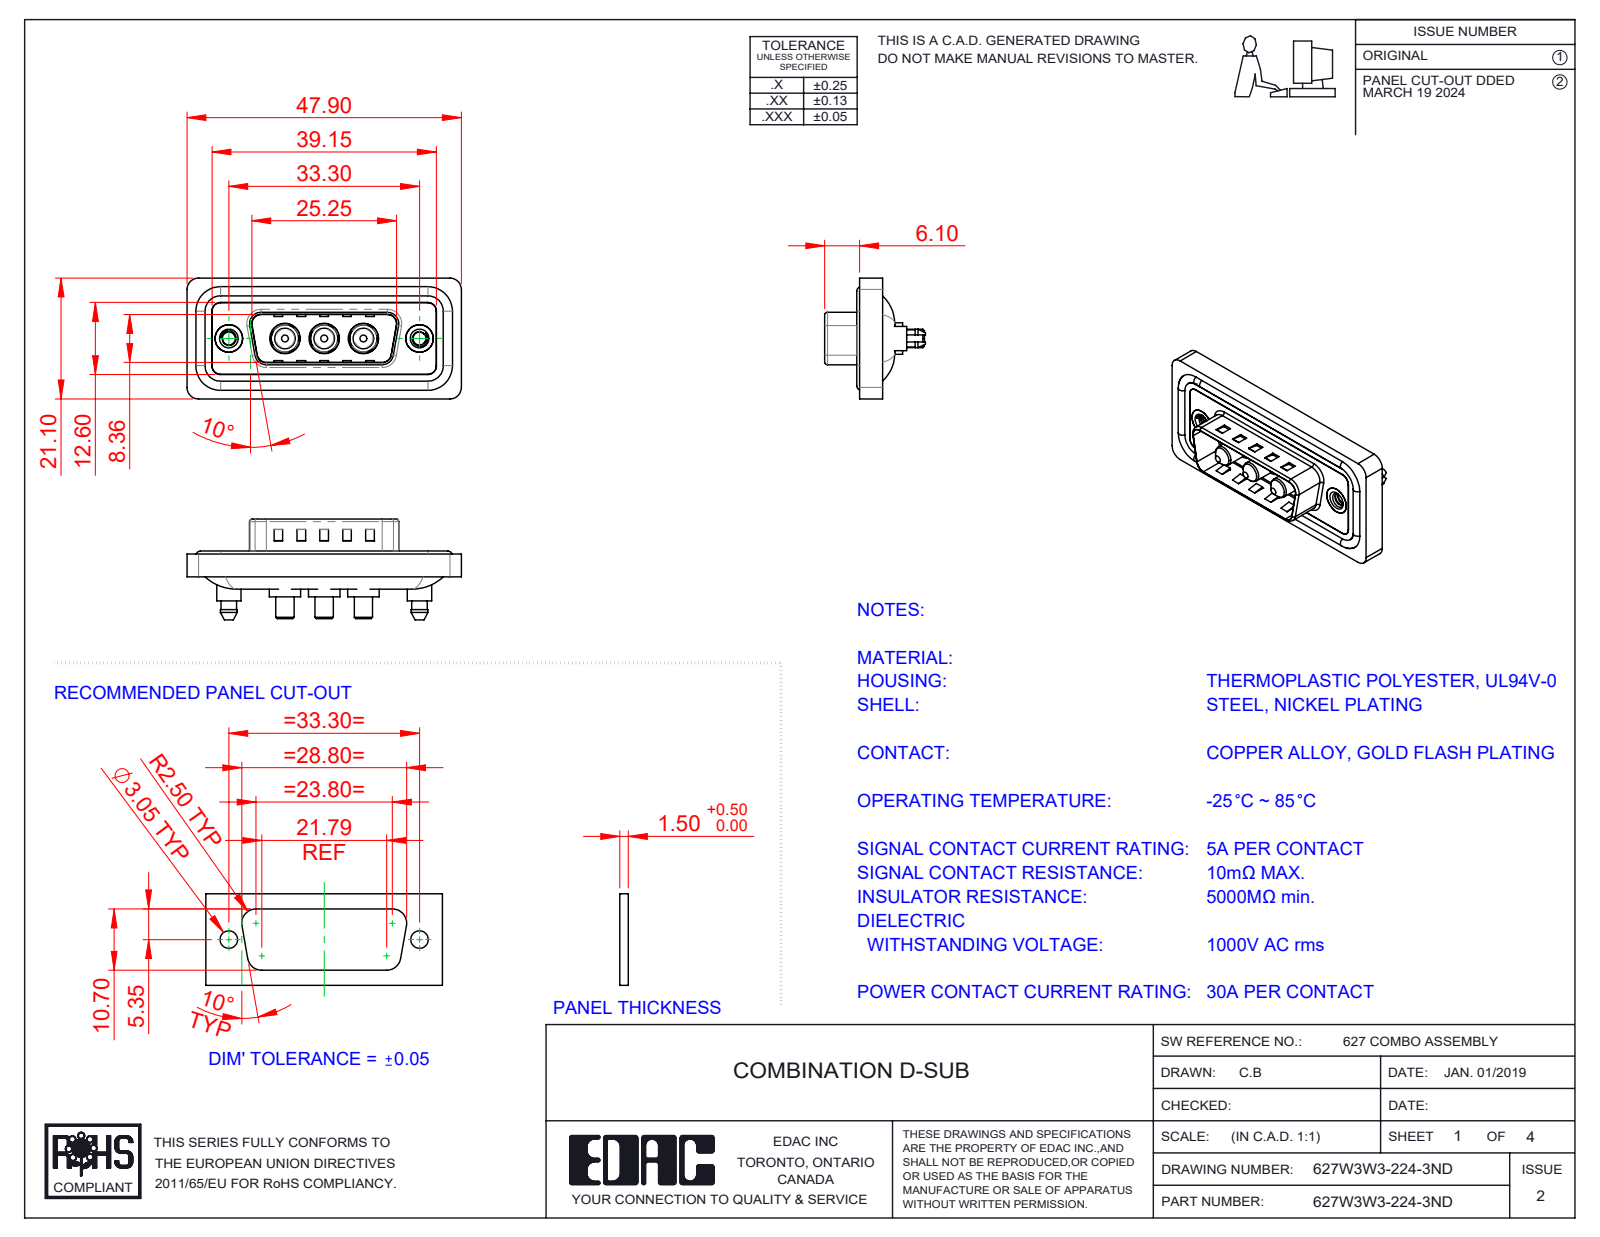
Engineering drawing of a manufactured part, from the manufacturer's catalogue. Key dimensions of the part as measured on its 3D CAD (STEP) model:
Part name (STEP PRODUCT): 627Combo Shell Rear_15 Contacts; 627Combo Threaded Boardlock_5; 627W3W3-224-3ND; Power Pin_30A S (+4 more)
STEP written by: SolidWorks 2023 (CONFIG_CONTROL_DESIGN)
Units: millimetres
Bodies: 13 solids, 622 faces (223 planar, 281 cylindrical, 118 other)
Overall size (bounding box): 47.9 × 21.1 × 17.6
Volume: 5 741 mm³ · Surface area: 9 103 mm²
Round holes (diameter × count): ⌀4.85 ×3, ⌀5.3 ×3, ⌀2.26 ×2, ⌀4 ×2, ⌀4.8 ×2, ⌀5 ×2
Round bosses / shafts (diameter × count): ⌀1.6 ×4, ⌀5.5 ×3, ⌀5.2 ×3, ⌀4.75 ×3, ⌀3.75 ×3, ⌀3.6 ×3, ⌀3.2 ×3, ⌀5.4 ×2
Partial cylindrical surfaces — rounded edges, fillets, slot ends (radius × count): R1.5 ×28, R2 ×20, R1.6 ×10, R0.5 ×8, R0.25 ×4, R0.6 ×4, R0.65 ×4, R0.9 ×4
Main face-to-face distances: 0.4, 1.1, 1.5, 3.1, 1.6, 0.5, 2.9, 4, 0.7, 0.82
Hole centre spacings: 6.85, 9.8, 16.65, 23.5, 13.7, 33.3
